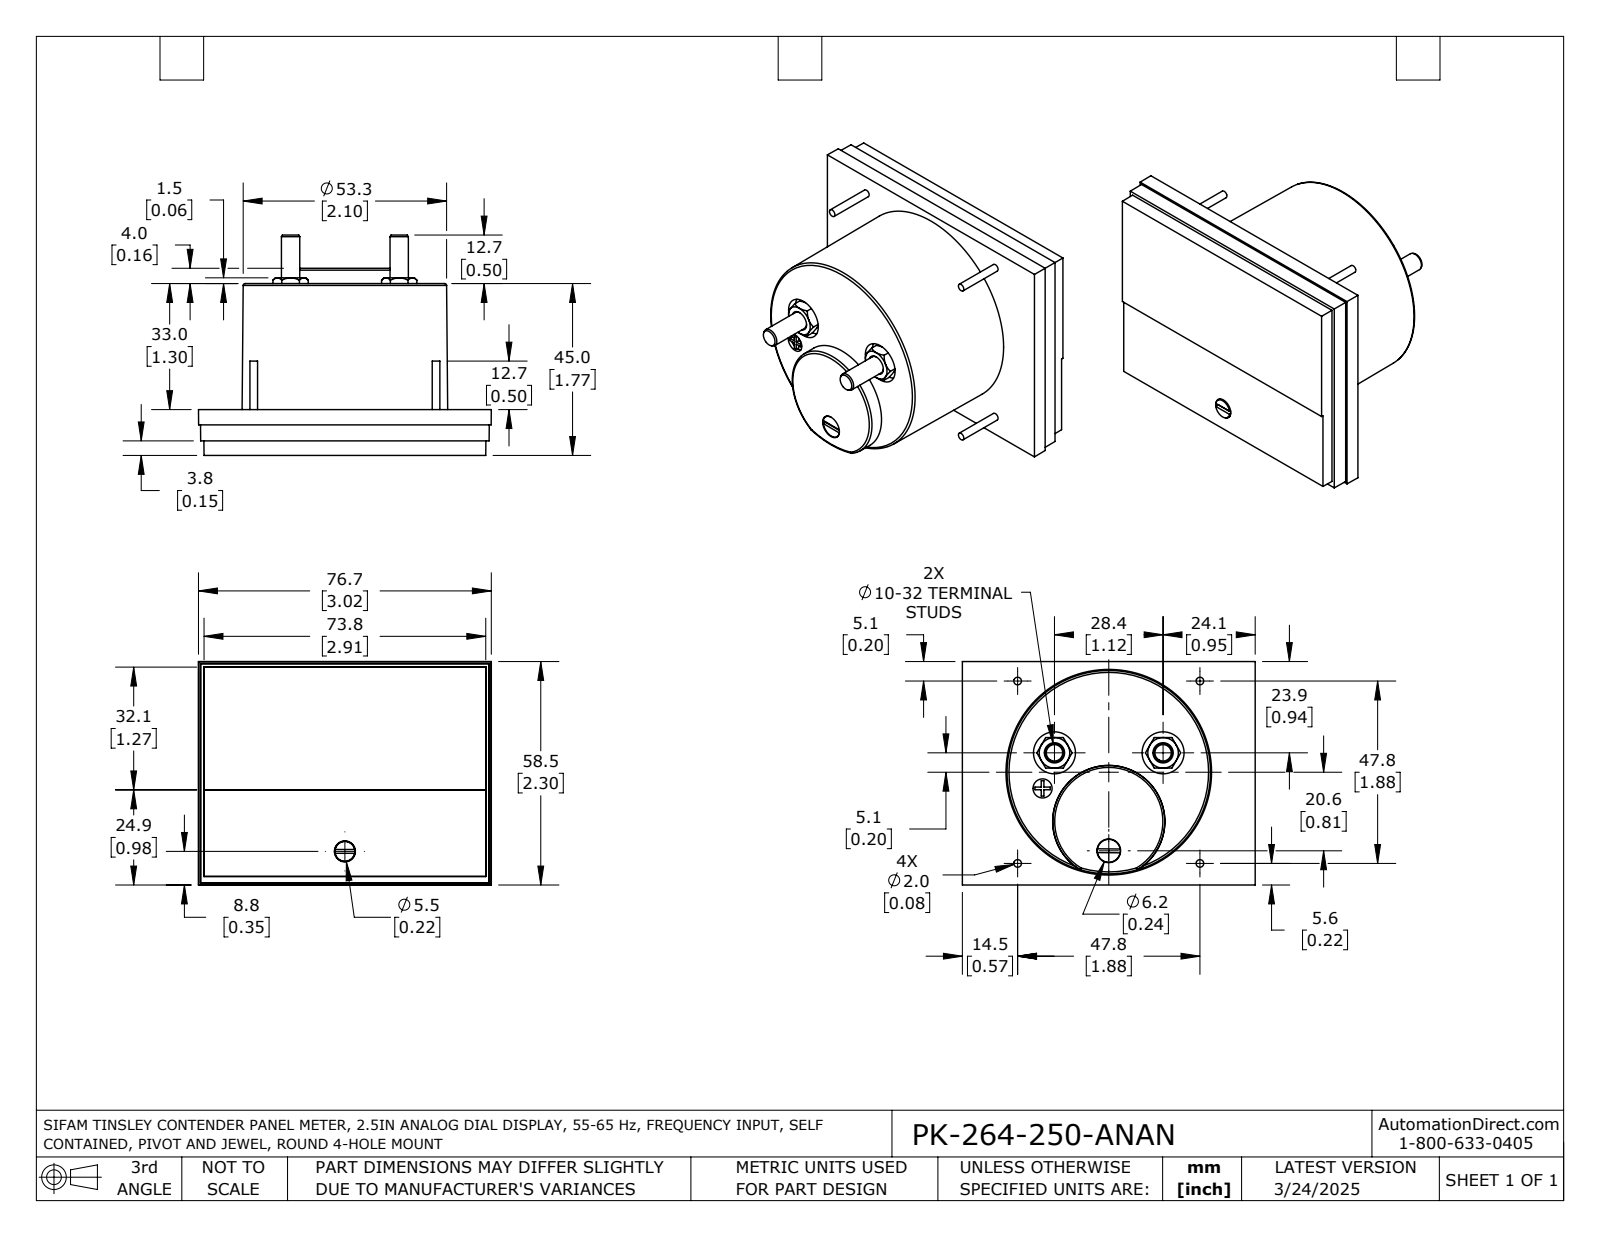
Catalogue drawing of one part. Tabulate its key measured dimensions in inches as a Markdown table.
| quantity | value |
| --- | --- |
| part name | PK-264-250-ANAN |
| STEP written by | SolidWorks 2021 (AUTOMOTIVE_DESIGN) |
| units | inches |
| bodies | 1 solid, 192 faces (95 planar, 37 cylindrical, 60 other) |
| overall size | 3.02 × 2.303 × 2.272 |
| volume | 7.657 in³ |
| surface area | 36.55 in² |
| round holes (diameter × count) | 0.197 × 3, 0.433 × 2, 0.209 × 1, 0.217 × 1, 0.244 × 1 |
| round bosses / shafts (diameter × count) | 0.079 × 4, 0.189 × 2, 0.236 × 1, 0.205 × 1 |
| partial cylindrical surfaces (radius × count) | 0.033 × 1 |
| main face-to-face distances | 0.02, 0.472, 0.13, 0.322, 0.15, 0.453, 0.057, 0.077, 0.396, 0.073 |
| hole center spacings | 1.155, 1.16, 0.387, 0.938, 0.942, 1.12, 1.295 |
